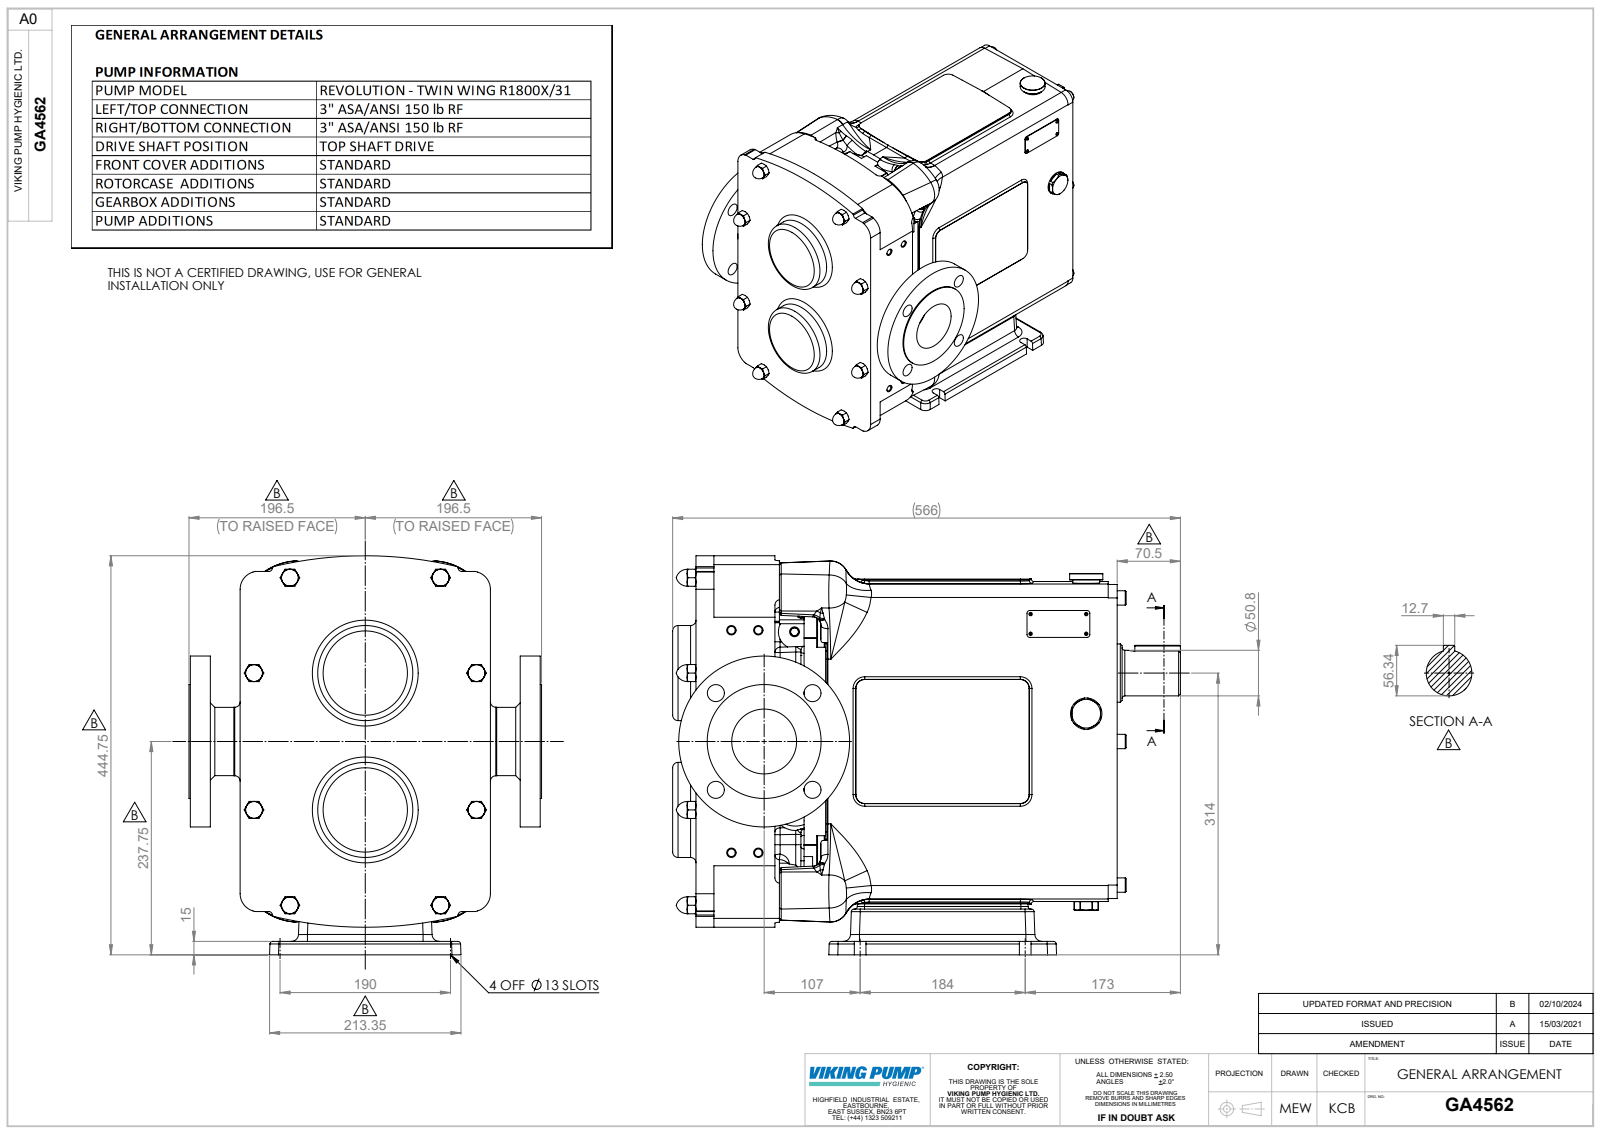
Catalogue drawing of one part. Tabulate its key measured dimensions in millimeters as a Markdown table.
| quantity | value |
| --- | --- |
| part name | Copy of Z94-5301-55 - 3 INCH ASA 150^GA4562; GA4562; Copy of R1800 CPP H TSD^GA4562 |
| STEP written by | SolidWorks 2023 (AUTOMOTIVE_DESIGN) |
| units | millimeters |
| bodies | 4 solids, 1719 faces (526 planar, 431 cylindrical, 762 other) |
| overall size | 566 × 444.75 × 393 |
| volume | 38 340 000 mm³ |
| surface area | 1 354 000 mm² |
| round holes (diameter × count) | 19 × 6, 8.5 × 4, 149 × 2, 35 × 1, 68.79 × 1, 72.3 × 1 |
| round bosses / shafts (diameter × count) | 14 × 10, 8 × 10, 16 × 6, 18 × 4, 187 × 2, 140 × 2, 106 × 2, 31.5 × 2 |
| partial cylindrical surfaces (radius × count) | 3 × 44, 6 × 36, 10 × 30, 0.2 × 24, 1 × 16, 5 × 16, 4 × 14, 8 × 10 |
| main face-to-face distances | 190, 469.5, 3, 193, 349, 120.5, 41.5, 44.5, 234.5, 237.5 |
| hole center spacings | 76.2, 107.76, 152.4, 30, 72.24, 84.63, 92.53, 107.71 |
